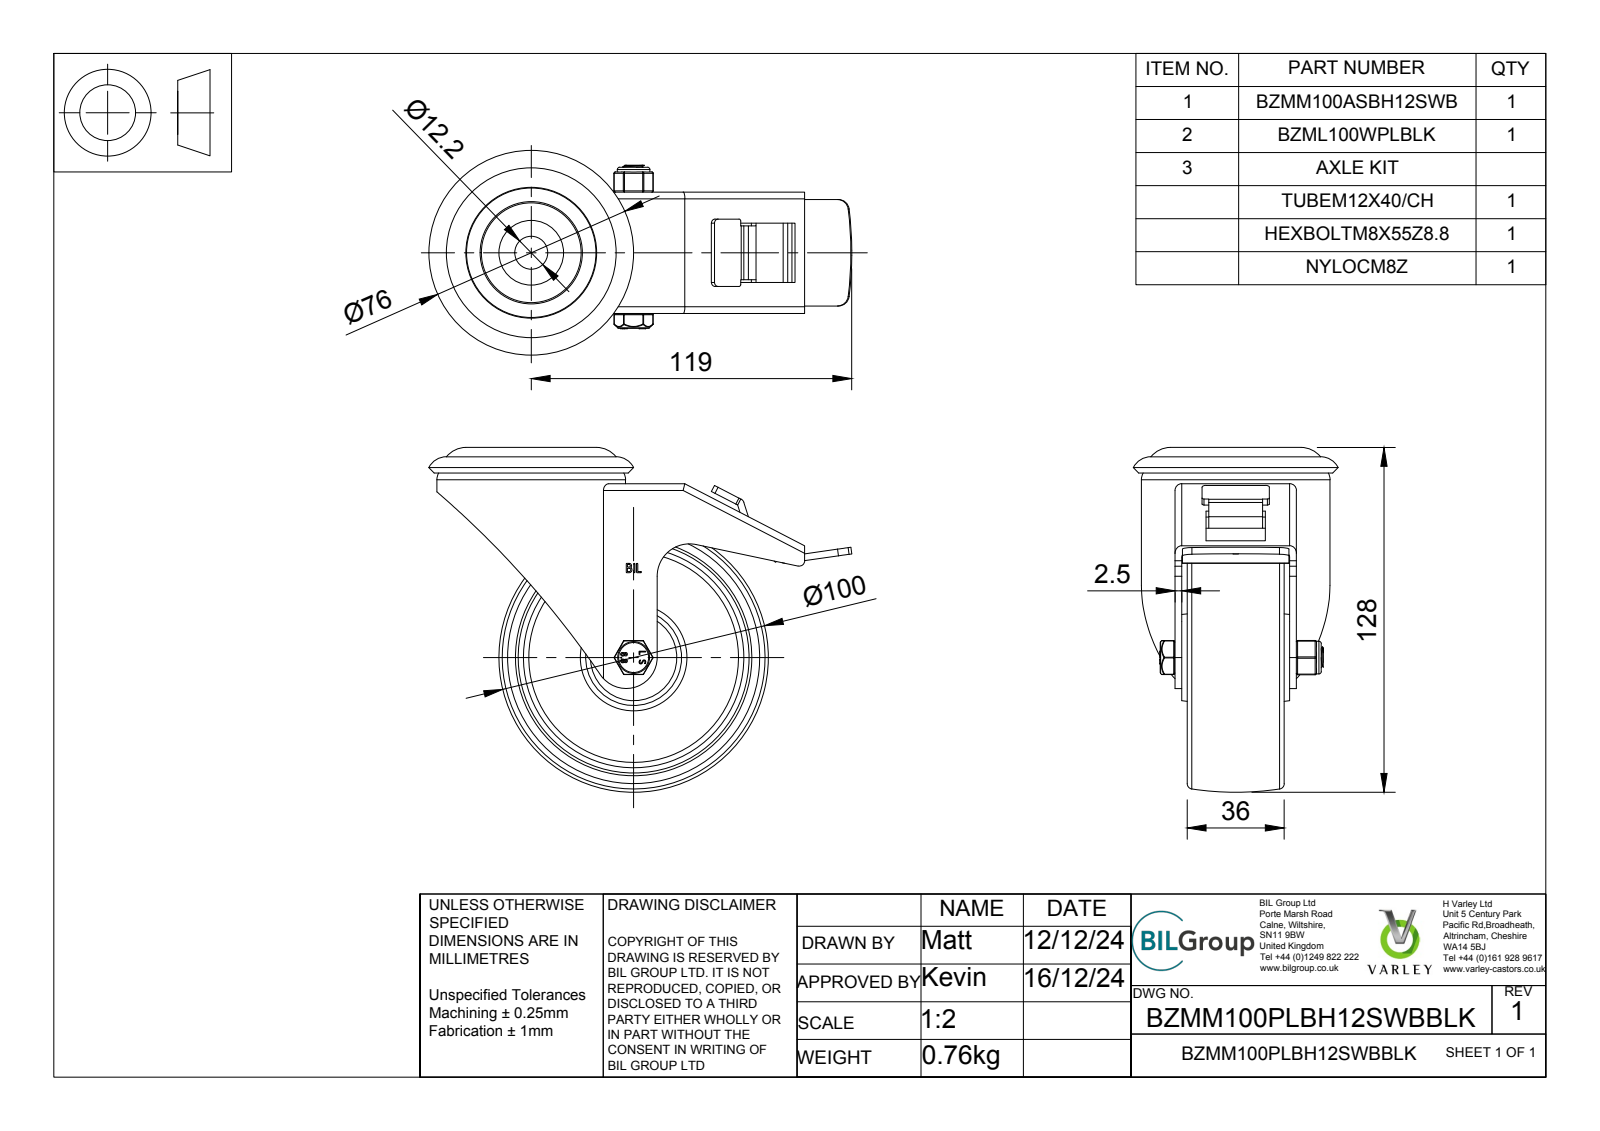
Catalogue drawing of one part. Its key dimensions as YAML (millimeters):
part_name: "BZMM100PLBH12SWBBLK v3; BZMM100ASBH12SWB v1; PRESSED STEEL, ZINC PLATED HEAD; PRESSED STEEL, ZINC PLATED FORKS (+8 more)"
step_written_by: "Autodesk Translation Framework v13.20.0.188 (AP242_MANAGED_MODEL_BASED_3D_ENGINEERING_MIM_LF)"
units: millimeters
bodies: {solids: 9, faces: 569, planar: 271, cylindrical: 194, other: 104}
overall_size: [157, 128, 76]
volume: 216724
surface_area: 104181
round_holes:
  - {diameter: 0.66, count: 2}
  - {diameter: 12.2, count: 2}
  - {diameter: 8, count: 1}
  - {diameter: 8.2, count: 1}
  - {diameter: 8.4, count: 1}
  - {diameter: 8.6, count: 1}
  - {diameter: 65, count: 1}
  - {diameter: 72, count: 1}
round_bosses_or_shafts:
  - {diameter: 70, count: 1}
  - {diameter: 49.5, count: 1}
  - {diameter: 38, count: 1}
  - {diameter: 24, count: 1}
  - {diameter: 21.31, count: 1}
  - {diameter: 12.1, count: 1}
  - {diameter: 11.9, count: 1}
  - {diameter: 11.5, count: 1}
partial_cylinders:
  - {radius: 0.75, count: 50}
  - {radius: 0.5, count: 18}
  - {radius: 0.25, count: 12}
  - {radius: 1.25, count: 10}
  - {radius: 0.33, count: 4}
  - {radius: 0.64, count: 4}
  - {radius: 2.5, count: 4}
  - {radius: 2, count: 3}
face_to_face_distances: [2.5, 17, 23, 19.5, 42.5, 25.5, 6, 4.5, 40, 2]
hole_center_spacings: [3.22, 2.49]
